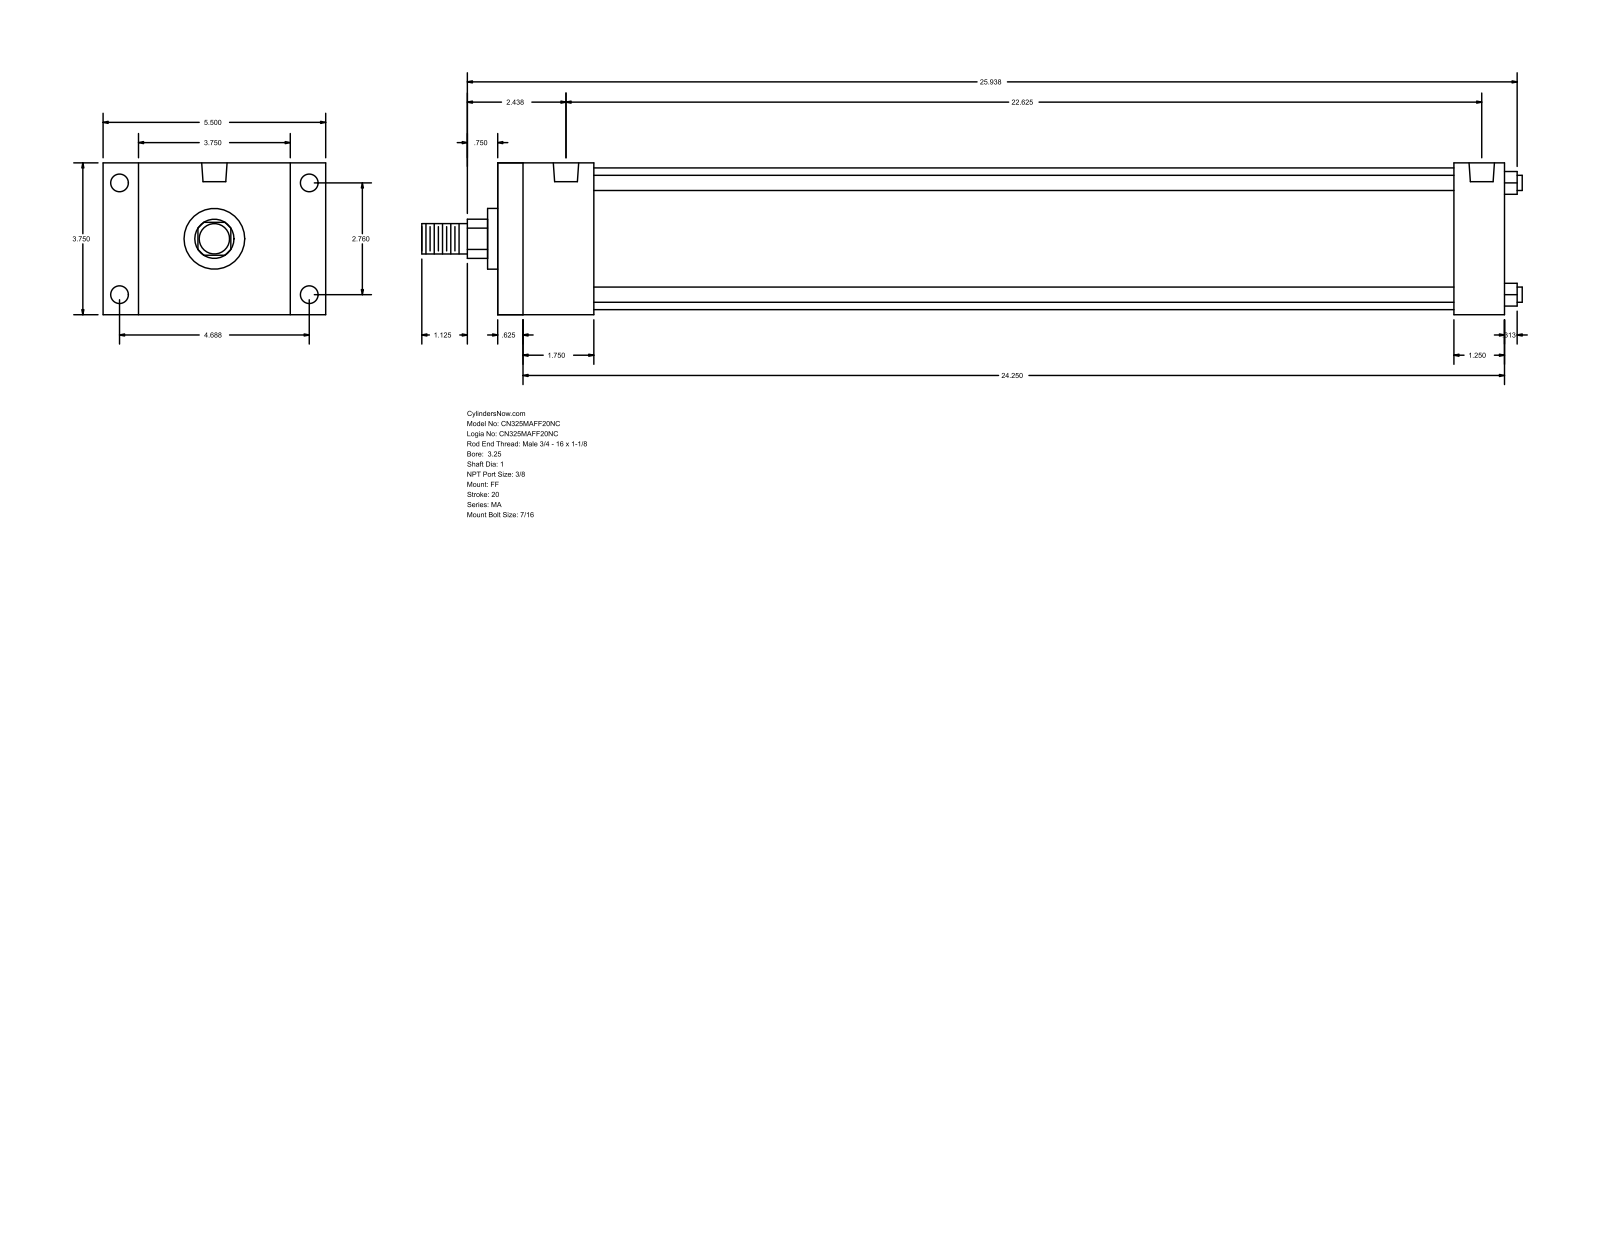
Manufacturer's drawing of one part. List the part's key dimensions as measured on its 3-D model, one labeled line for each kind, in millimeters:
Part name (STEP PRODUCT): MA_FF__0325_1
STEP written by: GSSL Pune (CONFIG_CONTROL_DESIGN)
Units: millimetres
Bodies: 0 solids, 92 faces (64 planar, 28 cylindrical, 0 other)
Overall size (bounding box): 690.56 × 139.7 × 95.25
Round holes (diameter × count): ⌀11.11 ×8, ⌀15.93 ×2
Round bosses / shafts (diameter × count): ⌀9.53 ×4, ⌀88.9 ×1, ⌀38.1 ×1, ⌀25.4 ×1, ⌀19.05 ×1
Partial cylindrical surfaces — rounded edges, fillets, slot ends (radius × count): R12.29 ×1
Main face-to-face distances: 95.24, 631.83, 15.87, 615.96, 22.23, 117.47, 60.33, 600.07, 44.46, 584.2
Hole centre spacings: 4.76, 70.1, 119.06, 138.16, 565.16, 569.92, 574.68
